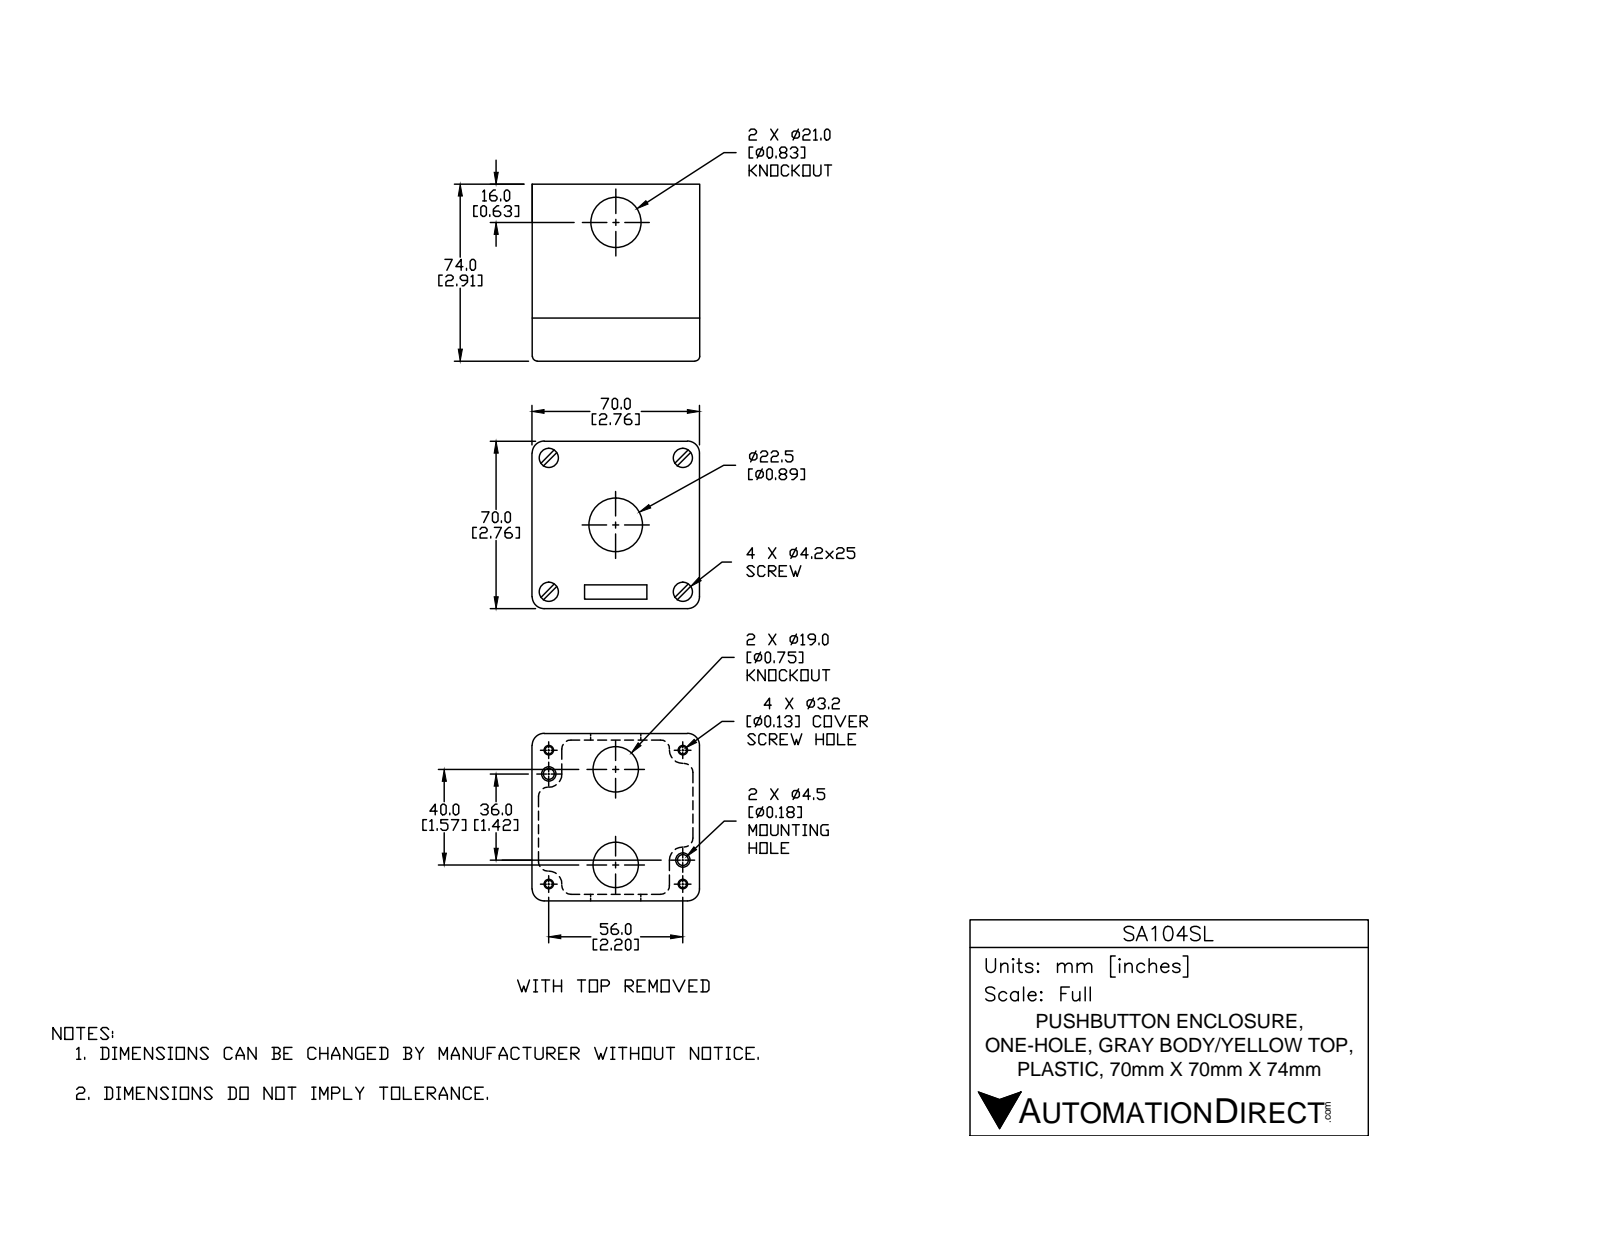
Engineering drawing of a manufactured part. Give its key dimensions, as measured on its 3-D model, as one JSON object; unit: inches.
{"part_name": "SA104SL", "step_written_by": "SolidWorks 2017 (AUTOMOTIVE_DESIGN)", "units": "inches", "bodies": {"solids": 6, "faces": 450, "planar": 121, "cylindrical": 178, "other": 151}, "overall_size": [2.922, 2.756, 2.756], "volume_in3": 7.101, "surface_area_in2": 95.1, "round_holes": [[0.126, 4], [0.165, 4], [0.315, 4], [0.177, 2], [0.295, 2], [0.748, 2], [0.827, 1], [0.886, 1]], "round_bosses_or_shafts": [[0.291, 4], [0.11, 4]], "partial_cylinders_radius": [[0.02, 16], [0.041, 8], [0.095, 8], [0.039, 4], [0.071, 4], [0.197, 4], [0.259, 4], [0.323, 4]], "face_to_face_distances": [2.756, 0.102, 2.654, 2.915, 2.552, 0.087, 2.829, 0.079, 2.837, 2.75], "hole_center_spacings": [1.146, 1.559, 2.188, 2.205, 0.394, 0.787, 1.105, 1.311]}
